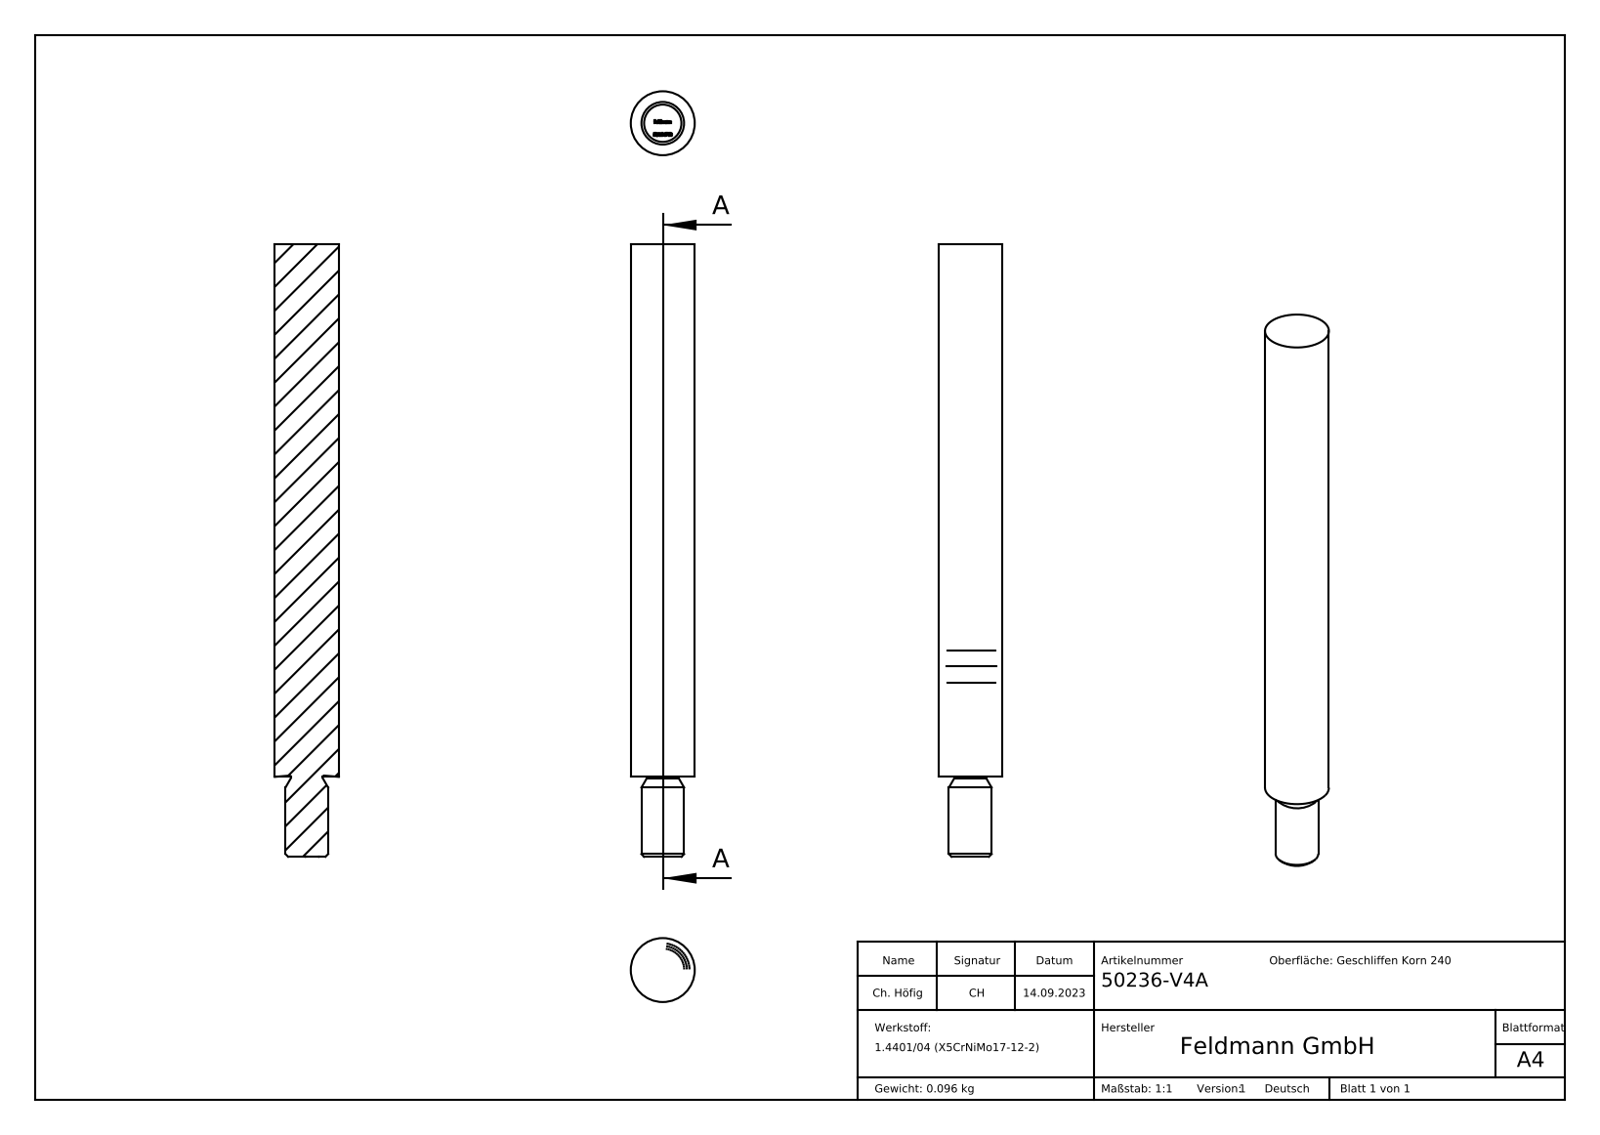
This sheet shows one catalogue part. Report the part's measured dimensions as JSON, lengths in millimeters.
{"part_name": "50236-V4A", "step_written_by": "SolidWorks 2018 (CONFIG_CONTROL_DESIGN)", "units": "millimeters", "bodies": {"solids": 1, "faces": 266, "planar": 157, "cylindrical": 2, "other": 107}, "overall_size": [115, 12, 12], "volume_mm3": 12025, "surface_area_mm2": 4394, "round_bosses_or_shafts": [[12, 1], [8, 1]], "face_to_face_distances": [115, 114.9, 0.77, 1.29, 2.38, 2.39, 0.72, 1.55, 2.44, 0.57]}
